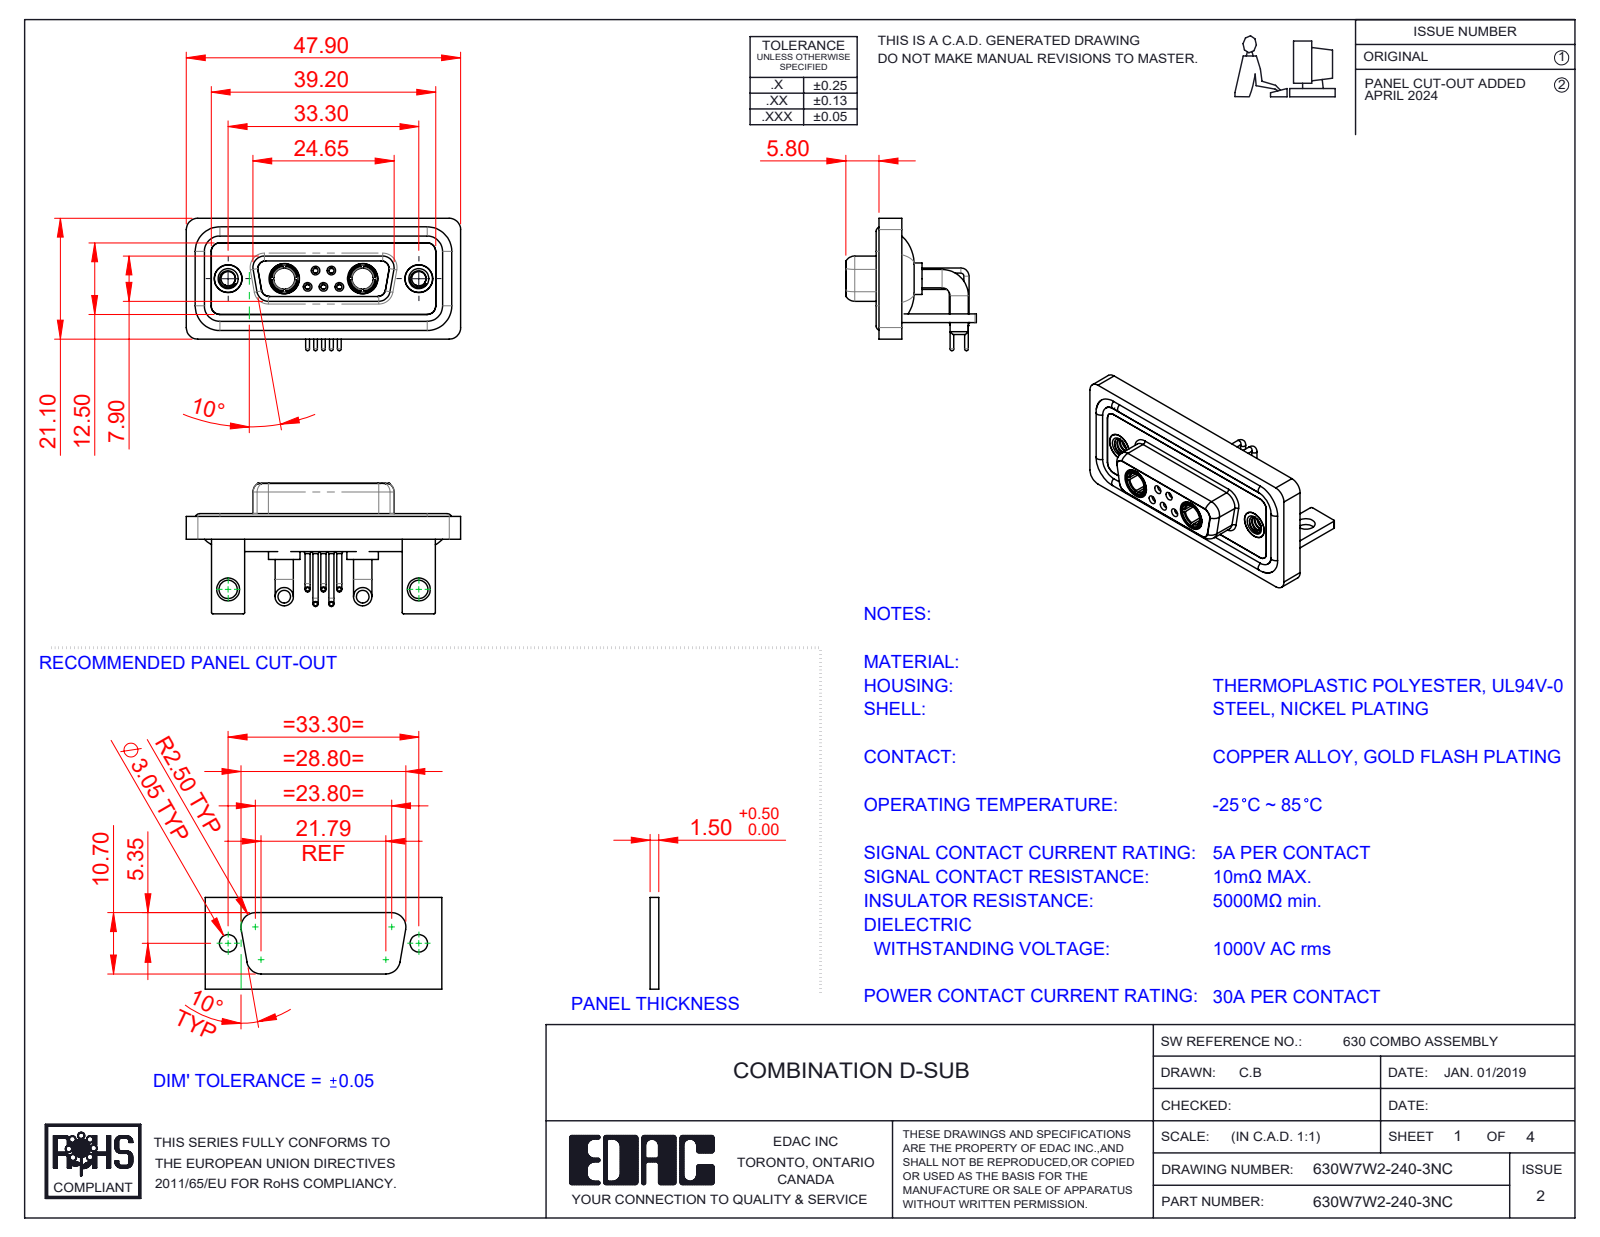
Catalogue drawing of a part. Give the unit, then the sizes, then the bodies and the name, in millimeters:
Units: millimetres
Overall size (bounding box): 47.9 × 23.12 × 22.8
Round holes (diameter × count): ⌀0.9 ×5, ⌀1.1 ×5, ⌀1.5 ×5, ⌀2 ×5, ⌀4.85 ×4, ⌀1.6 ×3, ⌀1.7 ×2, ⌀2.5 ×2, ⌀3.2 ×2, ⌀3.7 ×2, ⌀4 ×2, ⌀4.05 ×2
Round bosses / shafts (diameter × count): ⌀1.6 ×6, ⌀0.9 ×5, ⌀0.65 ×5, ⌀3.2 ×4, ⌀5.5 ×2, ⌀5.2 ×2, ⌀4.96 ×2, ⌀4.95 ×2
Partial cylindrical surfaces — rounded edges, fillets, slot ends (radius × count): R2 ×21, R1.5 ×18, R0.25 ×16, R1.35 ×12, R1.6 ×8, R0.5 ×5, R0.6 ×4, R0.65 ×4
Main face-to-face distances: 0.4, 2.9, 1.5, 1.8, 3.7, 1.1, 4.1, 1.6, 2.5, 1.4
Hole centre spacings: 3.16, 2.77, 9.8, 23.5, 33.3, 4.31, 4.33, 5.03
Volume: 6 612 mm³ · Surface area: 10 981 mm²
Bodies: 18 solids, 849 faces (258 planar, 375 cylindrical, 216 other)
Part name (STEP PRODUCT): 630Combo Shell Front_15 Contacts; 630Combo Contact Row 1_50 Contacts; 630Combo Contact Row 2_50 Contacts; 630Combo Stabilizer Bracket_50 Contacts (+6 more)
STEP written by: SolidWorks 2023 (CONFIG_CONTROL_DESIGN)
